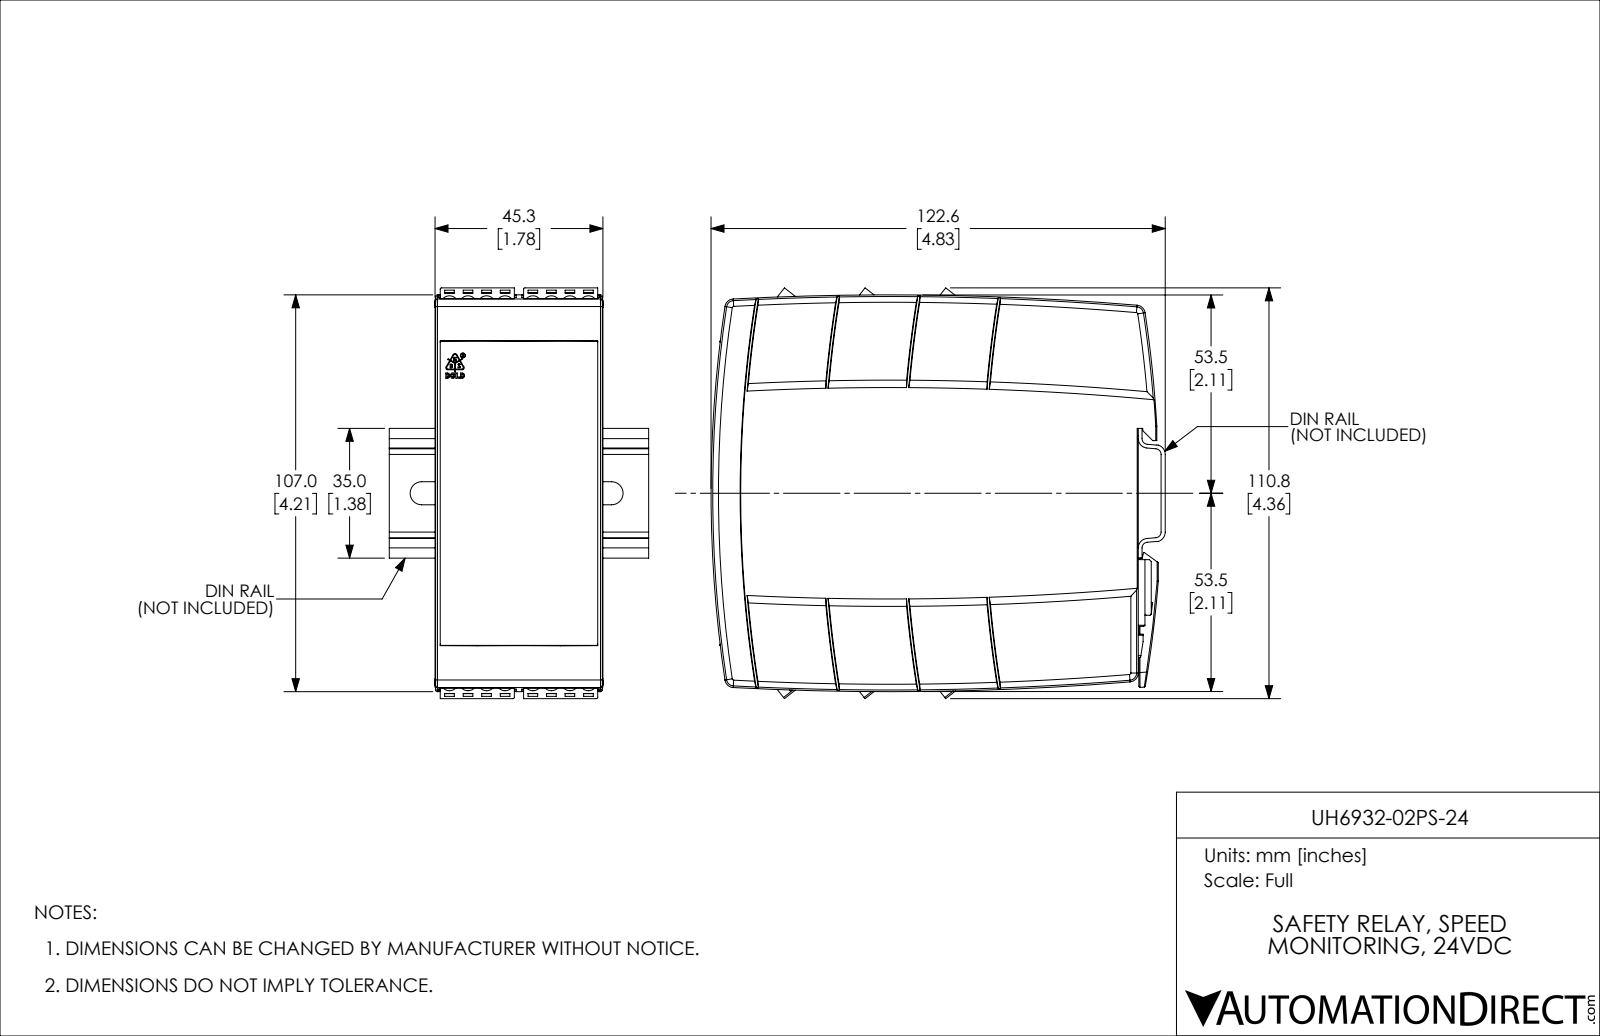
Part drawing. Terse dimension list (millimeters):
name: UH6932-02PS-24
written by: SolidWorks 2018 (AUTOMOTIVE_DESIGN)
unit: mm
bodies: 13 solids, 9557 faces (7531 planar, 1760 cylindrical, 266 other)
size: 120.7 × 110.8 × 45.3
volume: 108 100 mm³; area: 119 900 mm²
holes: 48× ⌀1.5, 48× ⌀3.2, 48× ⌀4, 6× ⌀0.7, 6× ⌀0.8, 1× ⌀1.2
bosses: 48× ⌀3.8, 6× ⌀2, 1× ⌀1.3
rounds: 48× R2.9, 37× R0.4, 18× R0.1, 18× R0.3, 18× R0.3, 18× R0.3, 12× R0.1, 12× R0.2
face distances: 1.1, 43.7, 42.6, 1.3, 43.9, 45.1, 17.1, 22.5, 44.9, 2
hole spacings: 5, 10, 22.5, 17.5, 27.5, 26.2, 12.5, 14.3
